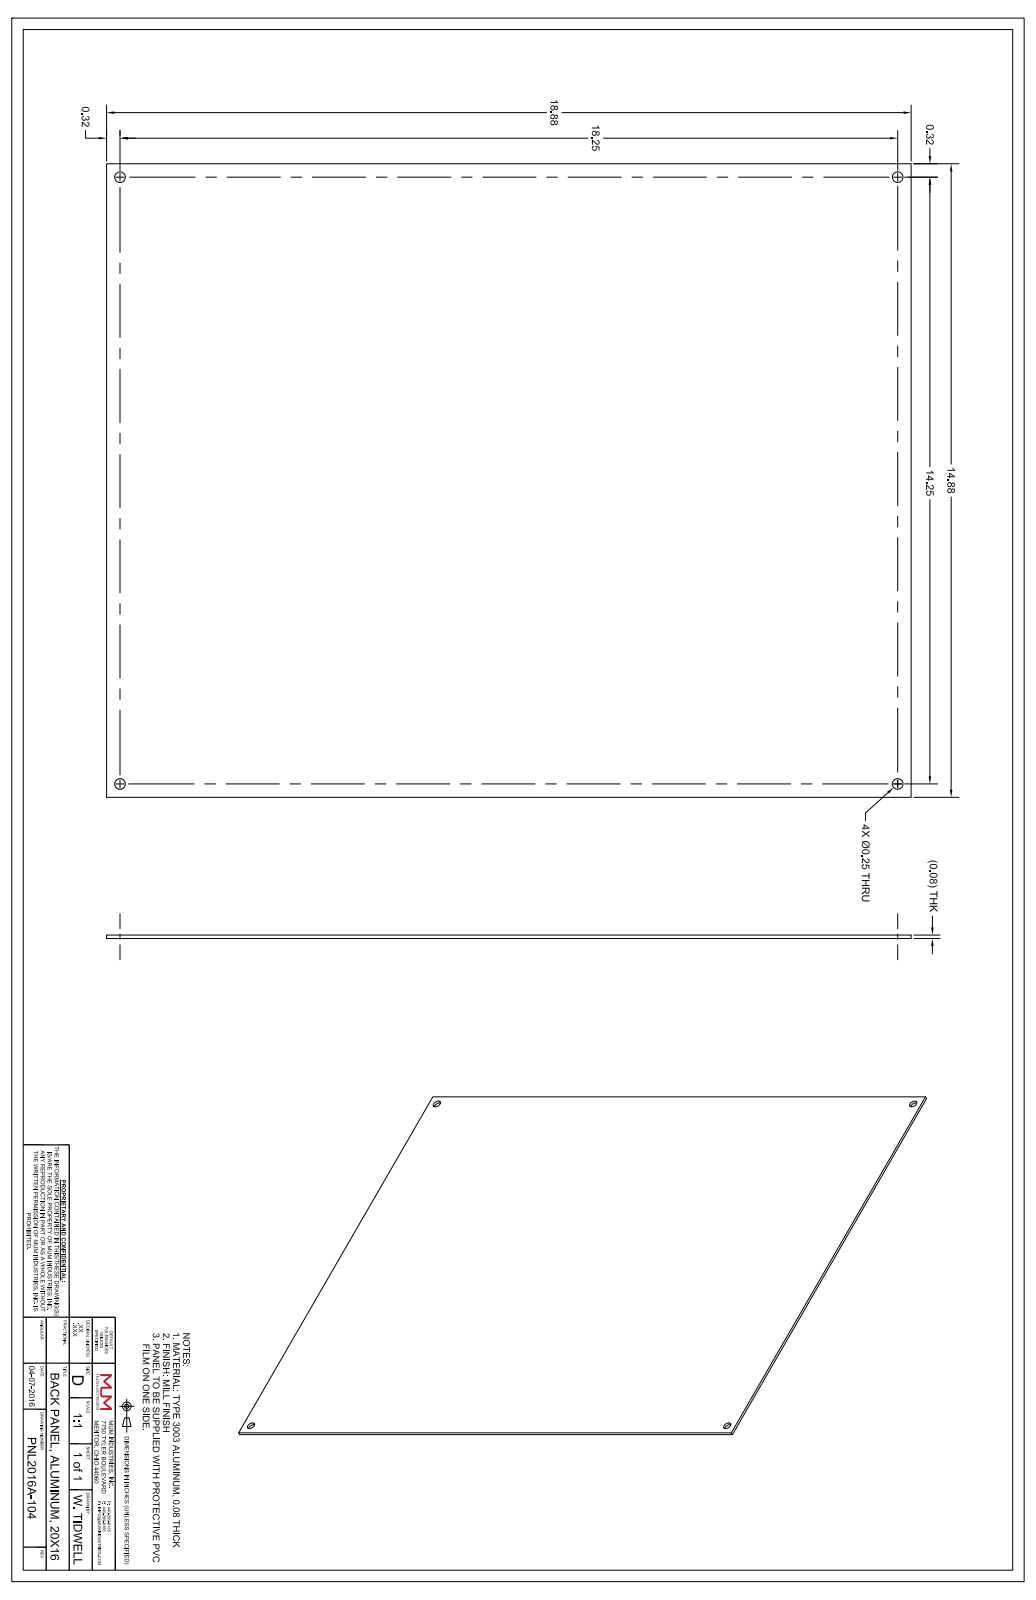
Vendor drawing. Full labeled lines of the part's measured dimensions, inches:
Part name (STEP PRODUCT): ABP-2016-P10
STEP written by: SolidWorks 2018 (AUTOMOTIVE_DESIGN)
Units: inches
Bodies: 1 solid, 10 faces (6 planar, 4 cylindrical, 0 other)
Overall size (bounding box): 18.88 × 14.88 × 0.08
Volume: 22.46 in³ · Surface area: 567.1 in²
Round holes (diameter × count): ⌀0.25 ×4
Main face-to-face distances: 0.08, 14.88, 18.88
Hole centre spacings: 14.25, 18.25, 23.154
